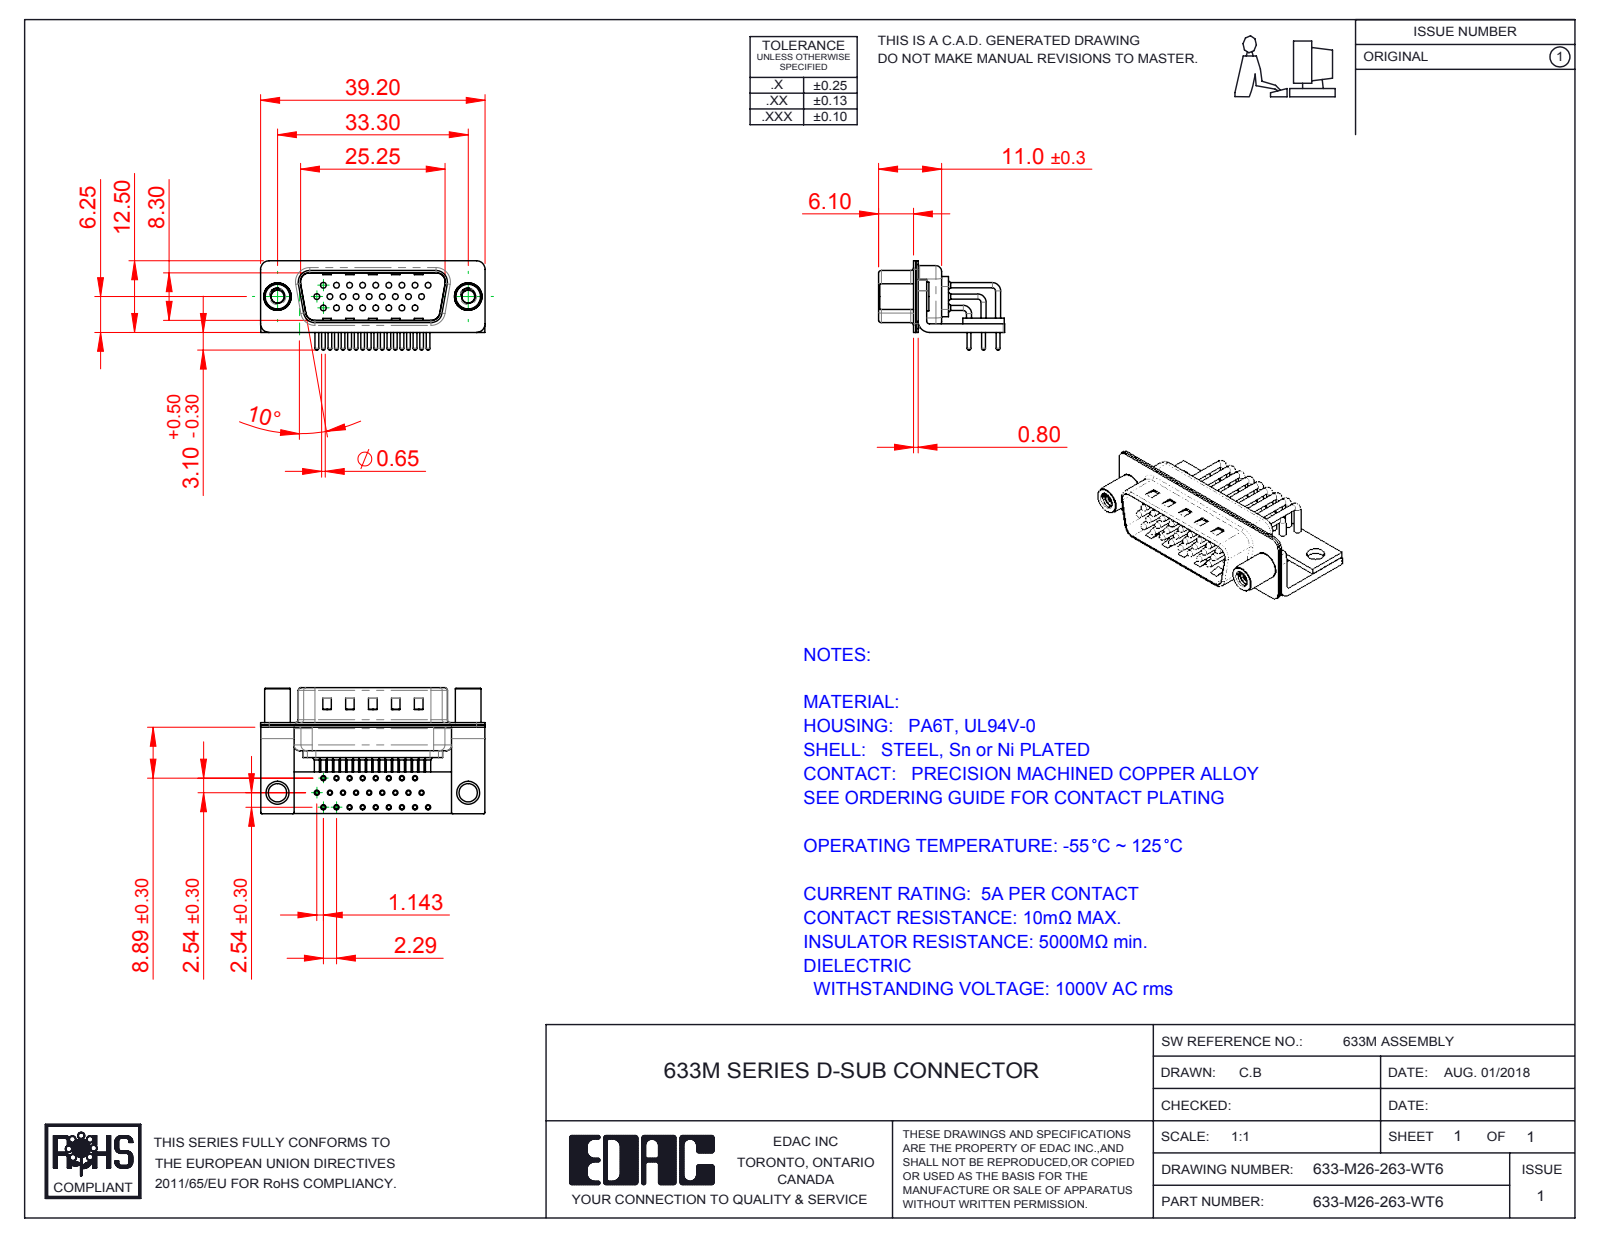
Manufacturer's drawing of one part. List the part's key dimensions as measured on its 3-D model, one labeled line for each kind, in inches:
Part name (STEP PRODUCT): 633M 4-40 Threaded Standoff; 633M Contact Row 3; 633M Shell Front_26 Contacts; 633M Stabilizer Bracket (+6 more)
STEP written by: SolidWorks 2016 (CONFIG_CONTROL_DESIGN)
Units: inches
Bodies: 34 solids, 3352 faces (1831 planar, 1185 cylindrical, 336 other)
Overall size (bounding box): 1.543 × 0.866 × 0.614
Volume: 0.168 in³ · Surface area: 12.89 in²
Round holes (diameter × count): ⌀0.035 ×26, ⌀0.039 ×26, ⌀0.067 ×26, ⌀0.079 ×26, ⌀0.089 ×2, ⌀0.126 ×2, ⌀0.157 ×2, ⌀0.189 ×2
Round bosses / shafts (diameter × count): ⌀0.059 ×26, ⌀0.035 ×26, ⌀0.026 ×26, ⌀0.197 ×2, ⌀0.193 ×2, ⌀0.177 ×2
Partial cylindrical surfaces — rounded edges, fillets, slot ends (radius × count): R0.04 ×26, R0.01 ×16, R0.059 ×16, R0.079 ×13, R0.02 ×9, R0.063 ×8, R0.024 ×4, R0.026 ×4
Main face-to-face distances: 0.016, 0.059, 0.033, 0.031, 0.049, 0.039, 0.075, 0.409, 0.376, 0.098
Hole centre spacings: 0.18, 0.09, 0.09, 0.156, 0.27, 0.168, 0.238, 0.109
